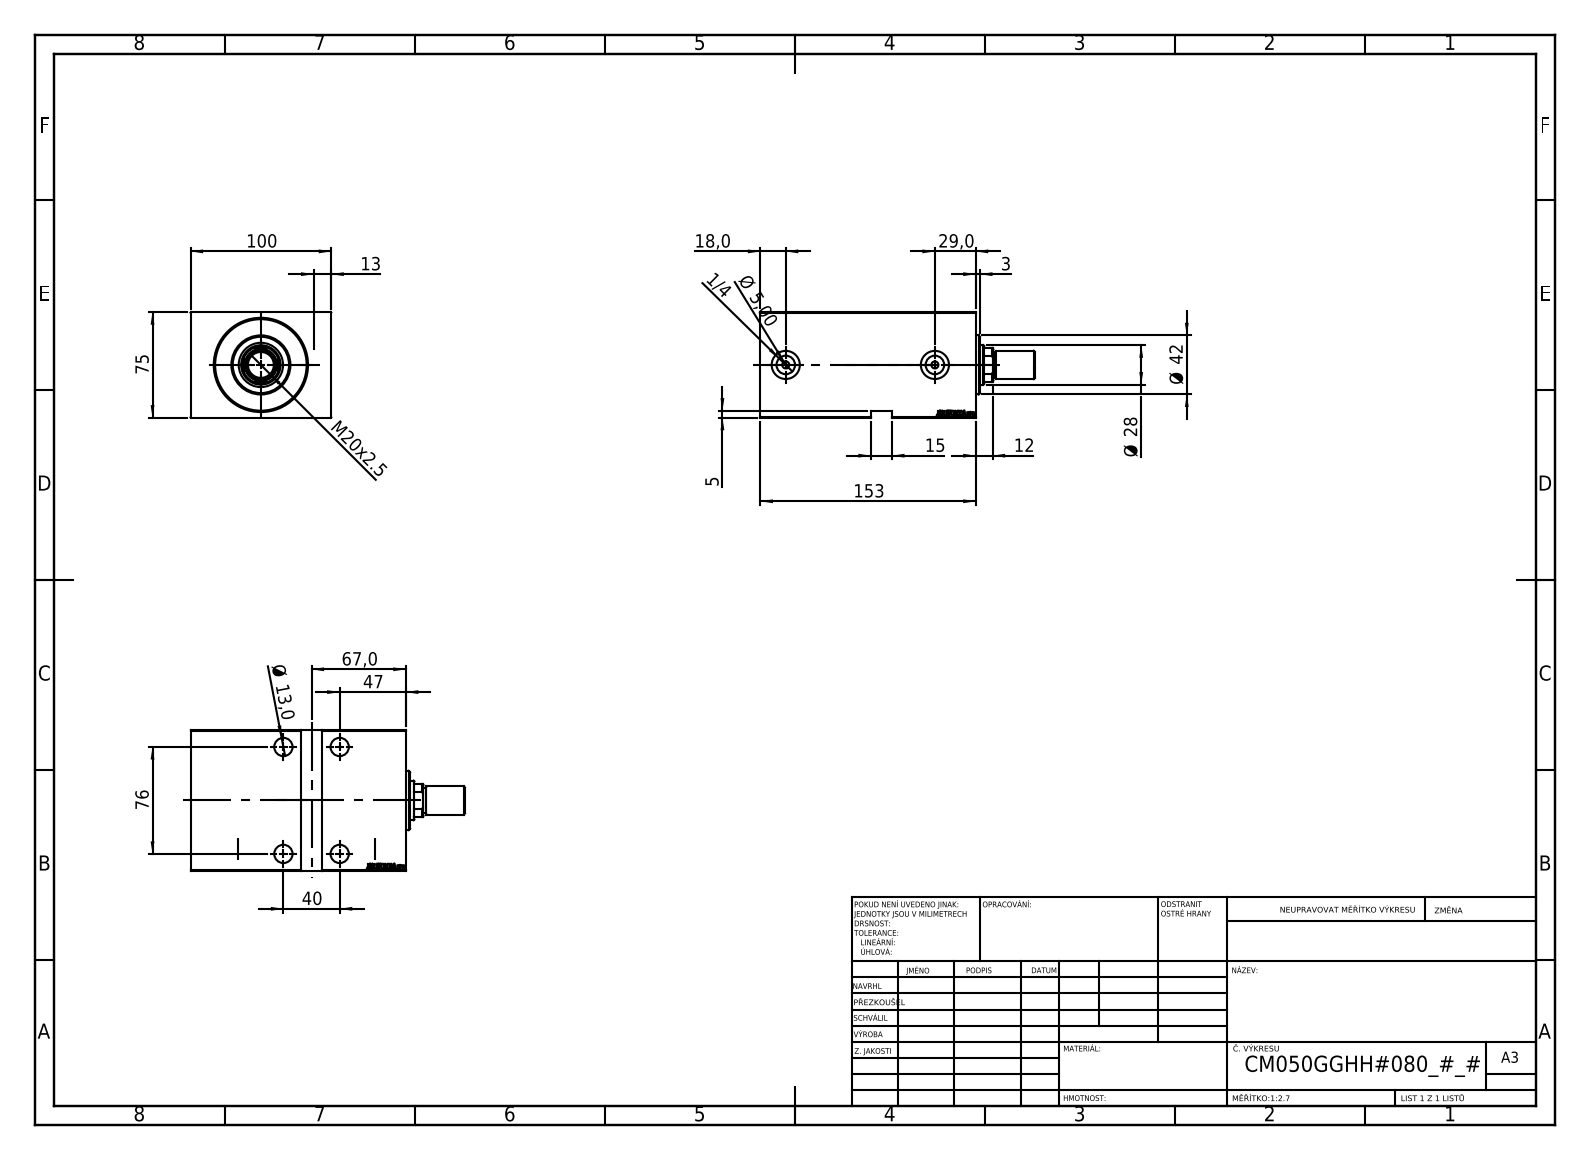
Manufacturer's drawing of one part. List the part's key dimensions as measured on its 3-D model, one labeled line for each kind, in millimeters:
Part name (STEP PRODUCT): Zatka_OIL_PORT; V450CM_MALE_METRIC; V450CM_G_VCP; V450CM_G_Body (+1 more)
STEP written by: SolidWorks 2019 (CONFIG_CONTROL_DESIGN)
Units: millimetres
Bodies: 6 solids, 908 faces (444 planar, 60 cylindrical, 404 other)
Overall size (bounding box): 195 × 100 × 75
Volume: 977 713 mm³ · Surface area: 139 441 mm²
Round holes (diameter × count): ⌀13 ×4, ⌀19 ×4, ⌀5 ×2, ⌀13.16 ×2, ⌀20 ×2, ⌀18.5 ×1, ⌀28 ×1, ⌀31.5 ×1, ⌀50 ×1, ⌀52 ×1, ⌀65 ×1
Round bosses / shafts (diameter × count): ⌀18 ×3, ⌀42 ×1, ⌀20 ×1
Partial cylindrical surfaces — rounded edges, fillets, slot ends (radius × count): R13.5 ×1
Main face-to-face distances: 75, 100, 153, 5, 134, 14, 139, 148, 47, 70
Hole centre spacings: 40, 76, 85.88, 106
